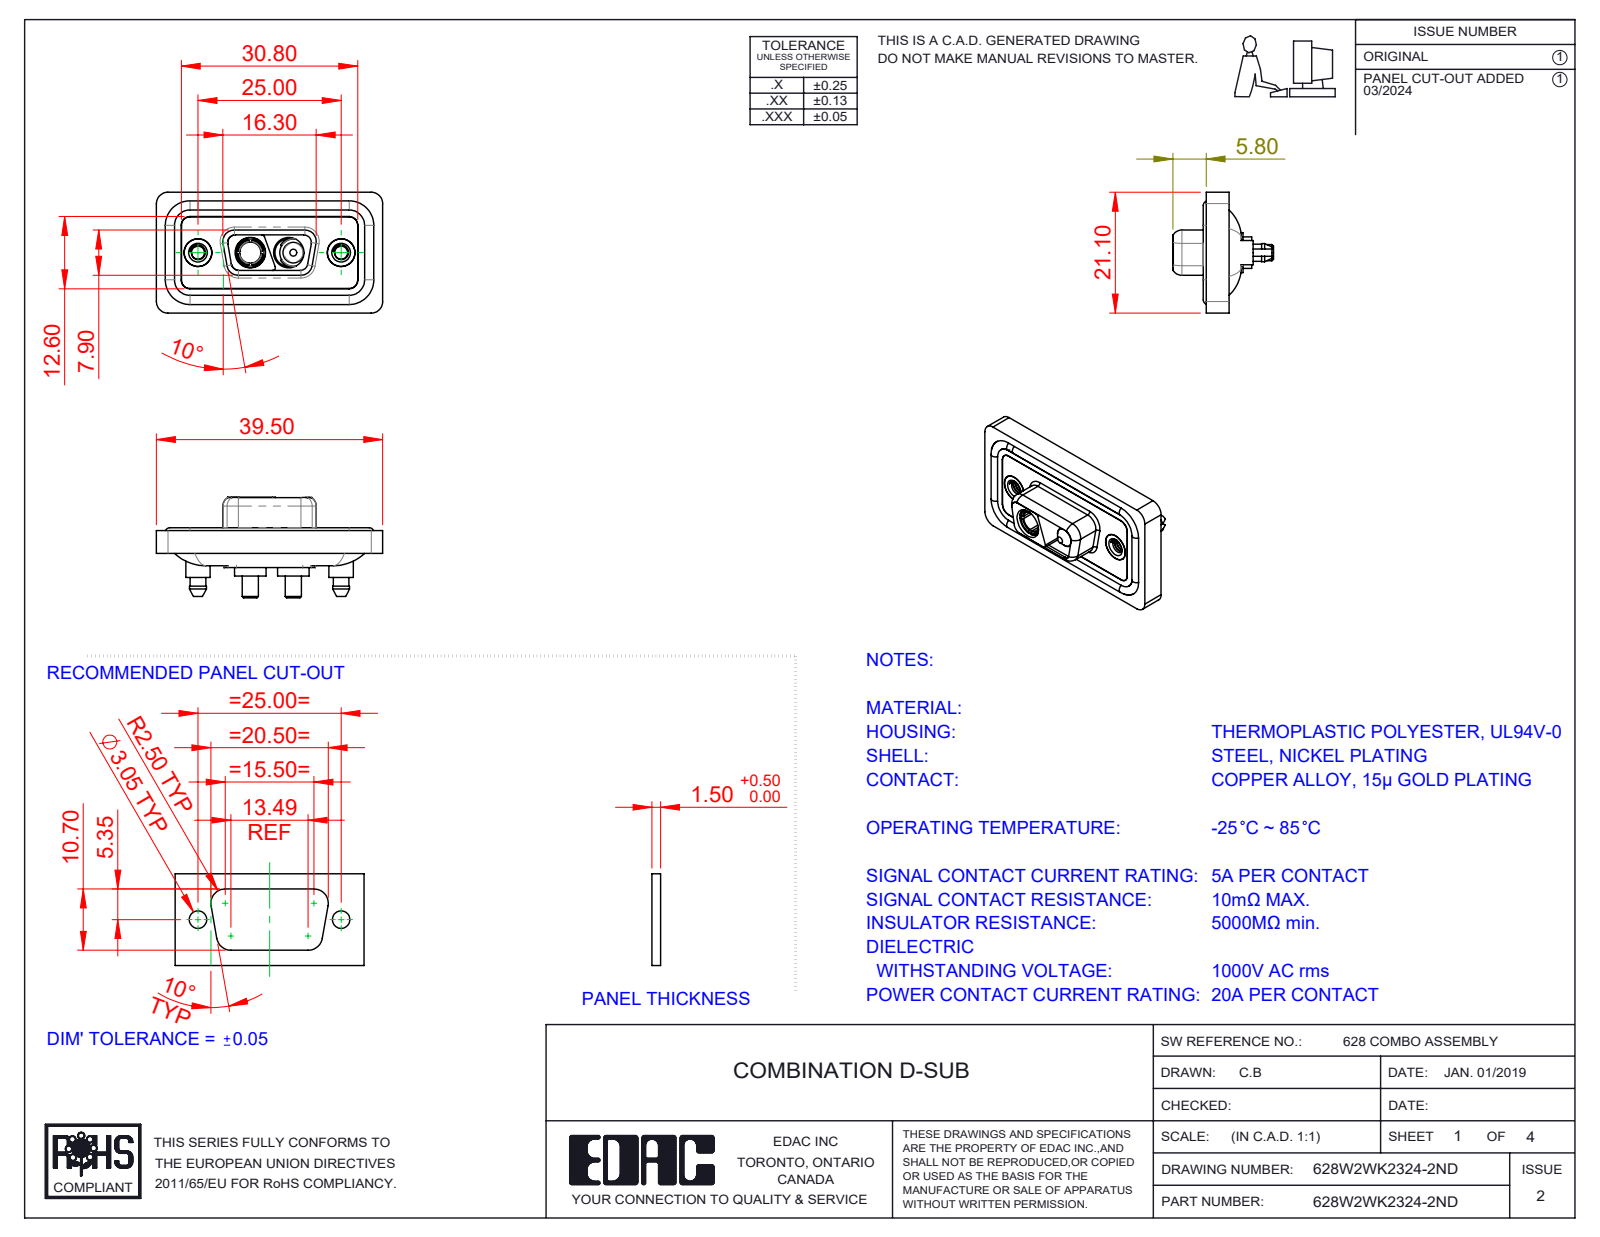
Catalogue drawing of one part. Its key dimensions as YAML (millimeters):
part_name: "628Combo Shell Front_09 Contacts; 628Combo Threaded Boardlock_D; 628Combo Housing_2WK2; 628Combo Waterproof Housing_09 Contacts (+4 more)"
step_written_by: "SolidWorks 2023 (CONFIG_CONTROL_DESIGN)"
units: millimeters
bodies: {solids: 11, faces: 566, planar: 160, cylindrical: 279, other: 127}
overall_size: [39.5, 21.1, 17.55]
volume: 4738
surface_area: 7683
round_holes:
  - {diameter: 4.85, count: 4}
  - {diameter: 2.26, count: 2}
  - {diameter: 4, count: 2}
  - {diameter: 4.05, count: 2}
  - {diameter: 5, count: 2}
  - {diameter: 5.3, count: 2}
  - {diameter: 3.7, count: 1}
round_bosses_or_shafts:
  - {diameter: 1.6, count: 4}
  - {diameter: 5.5, count: 2}
  - {diameter: 5.4, count: 2}
  - {diameter: 5.2, count: 2}
  - {diameter: 4.95, count: 2}
  - {diameter: 4.8, count: 2}
  - {diameter: 4.75, count: 2}
  - {diameter: 4.25, count: 2}
partial_cylinders:
  - {radius: 1.5, count: 24}
  - {radius: 2, count: 18}
  - {radius: 1.6, count: 10}
  - {radius: 1.35, count: 8}
  - {radius: 0.5, count: 6}
  - {radius: 0.25, count: 4}
  - {radius: 0.6, count: 4}
  - {radius: 0.65, count: 4}
face_to_face_distances: [0.4, 1.1, 2.9, 1.6, 0.5, 1.8, 5.65, 1.5, 4, 5.35]
hole_center_spacings: [9.14, 15.86, 6.72, 25]
